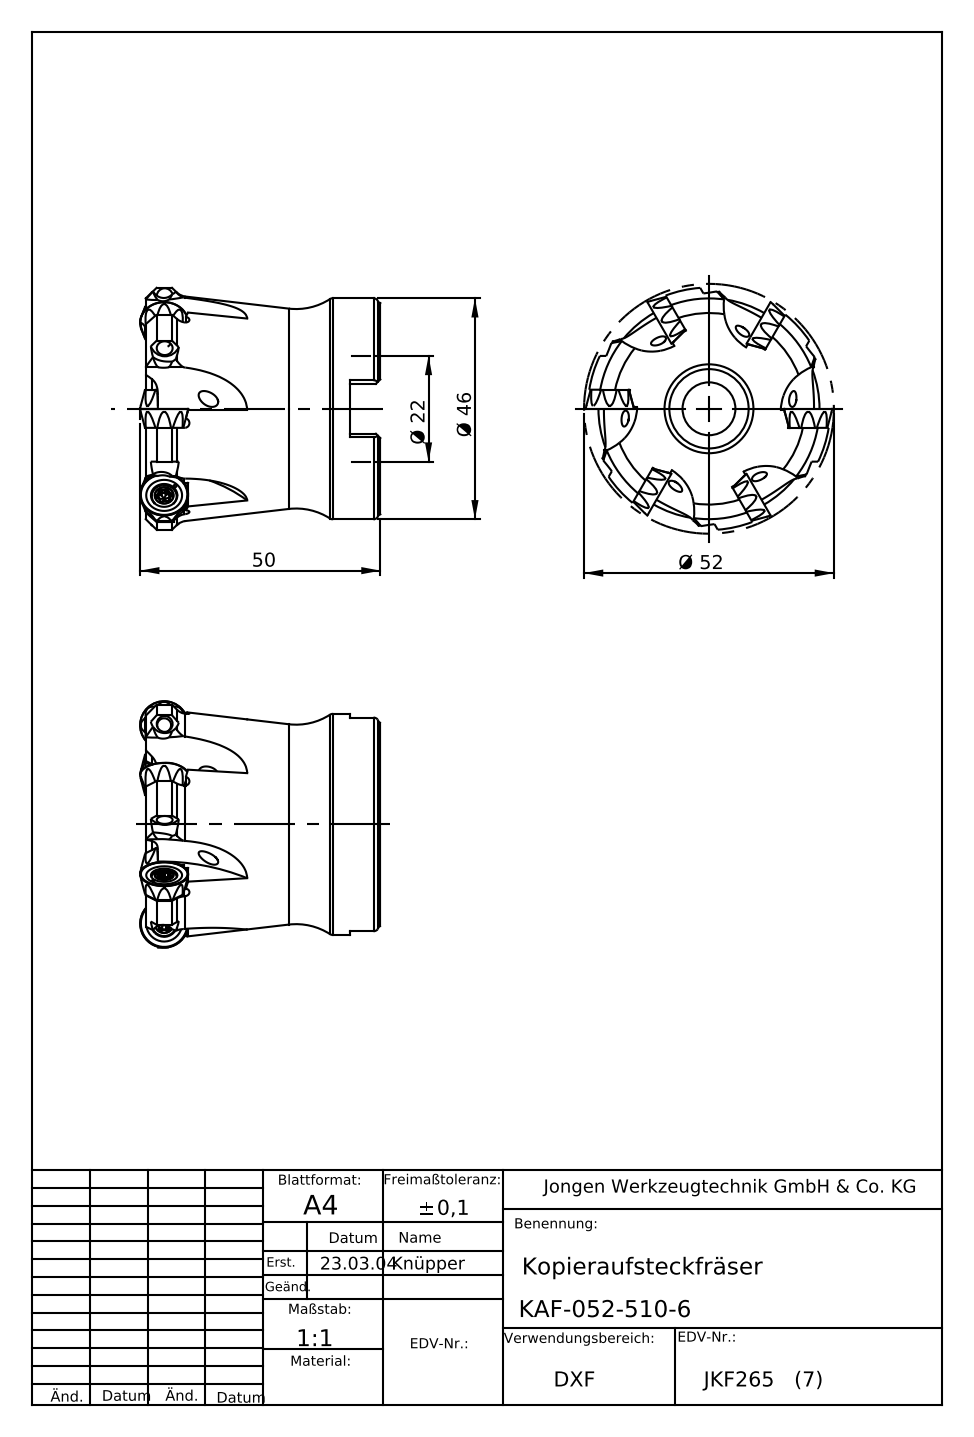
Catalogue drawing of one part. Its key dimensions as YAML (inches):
part_name: "KAF-052-510-6"
step_written_by: "SolidWorks 2012 (AUTOMOTIVE_DESIGN)"
units: inches
bodies: {solids: 1, faces: 172, planar: 86, cylindrical: 40, other: 46}
overall_size: [2.047, 2.047, 1.969]
volume: 3.711
surface_area: 23.93
round_holes:
  - {diameter: 0.118, count: 6}
  - {diameter: 0.433, count: 1}
  - {diameter: 0.65, count: 1}
  - {diameter: 0.866, count: 1}
  - {diameter: 0.872, count: 1}
  - {diameter: 0.878, count: 1}
round_bosses_or_shafts:
  - {diameter: 1.811, count: 1}
partial_cylinders:
  - {radius: 0.039, count: 6}
face_to_face_distances: [1.824, 0.248, 1.576, 0.906, 0.657, 0.919, 0.024, 0.409, 0.193, 0.217]
